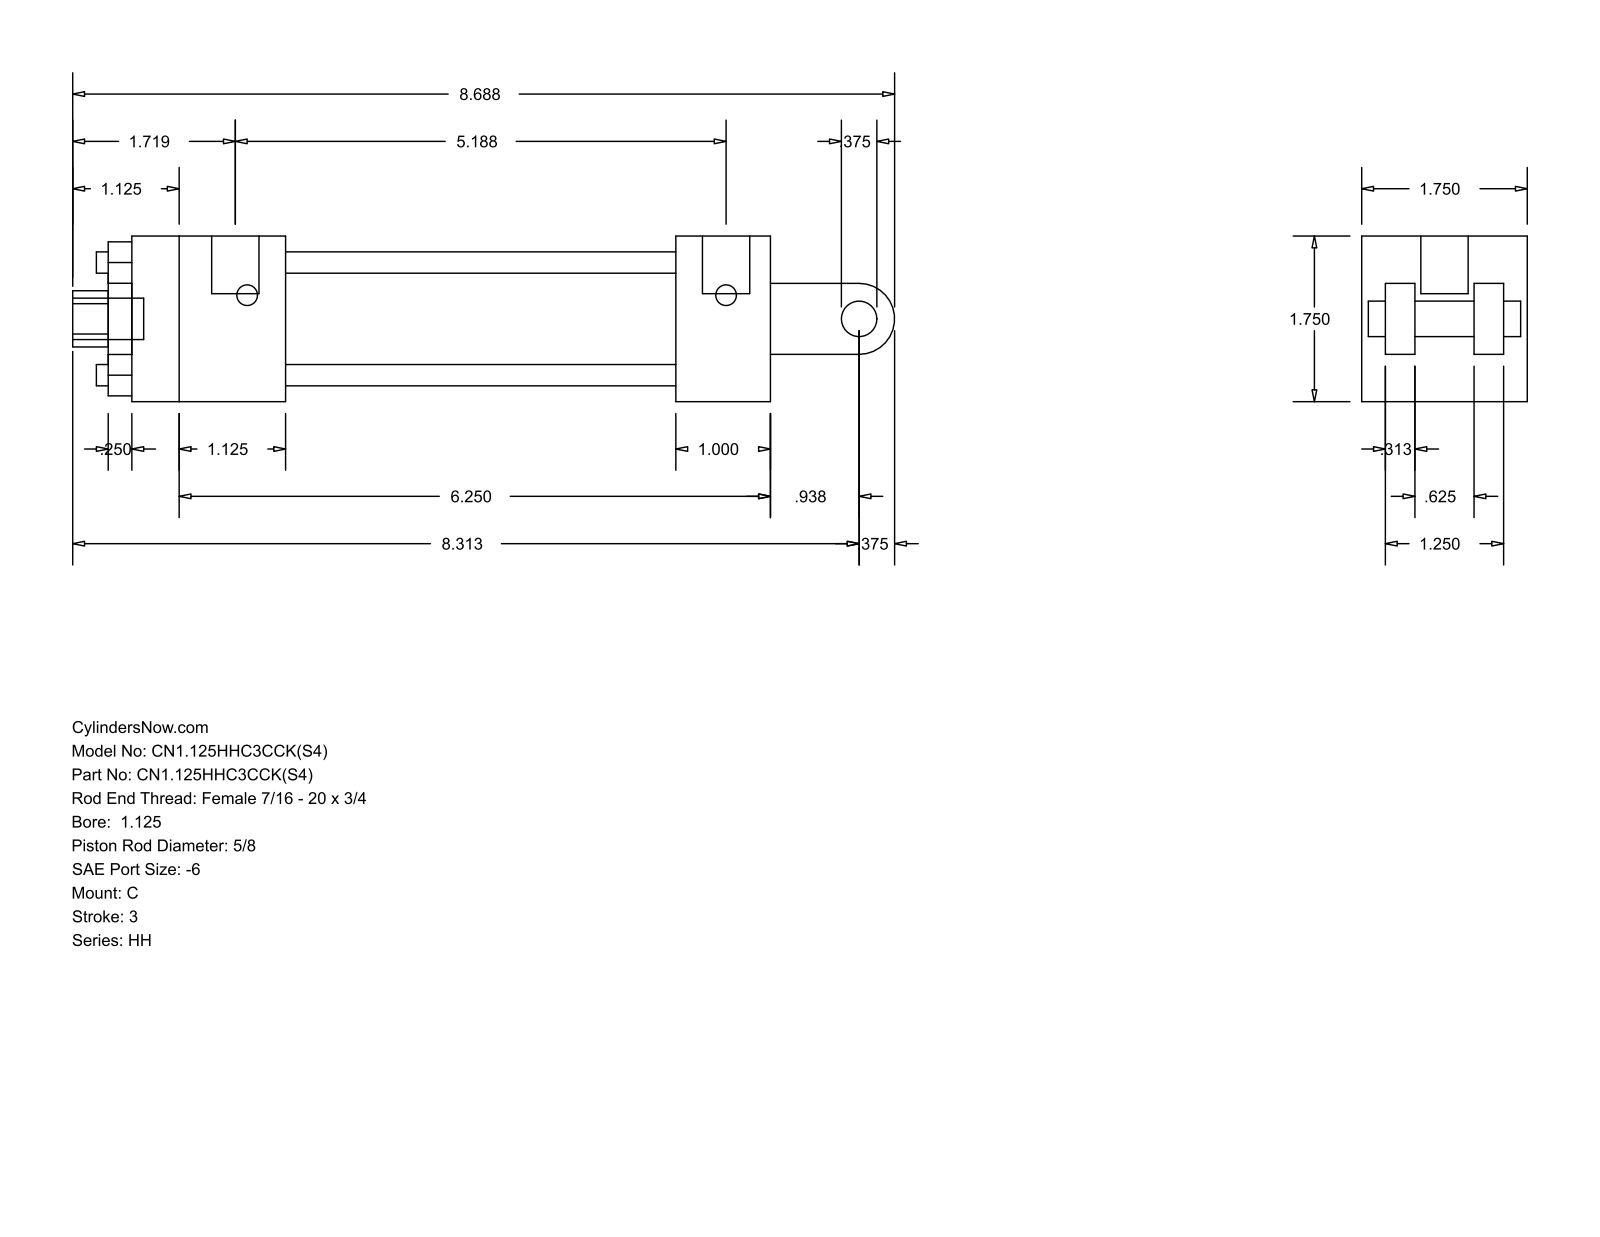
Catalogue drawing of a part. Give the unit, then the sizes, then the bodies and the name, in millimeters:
Units: millimetres
Overall size (bounding box): 220.66 × 44.45 × 44.45
Round holes (diameter × count): ⌀5.71 ×4, ⌀5.56 ×2, ⌀12.7 ×1, ⌀15.88 ×1, ⌀28.57 ×1, ⌀34.92 ×1
Round bosses / shafts (diameter × count): ⌀5.56 ×2, ⌀12.7 ×1, ⌀11.11 ×1, ⌀9.53 ×1
Partial cylindrical surfaces — rounded edges, fillets, slot ends (radius × count): R7.54 ×1, R9.53 ×1
Main face-to-face distances: 44.46, 6.35, 31.76, 14.29, 12.7, 30.17, 38.11, 7.94, 23.82, 41.27
Hole centre spacings: 21.37, 30.22, 42.74
Bodies: 0 solids, 99 faces (70 planar, 29 cylindrical, 0 other)
Part name (STEP PRODUCT): HH_C__0112_0.625
STEP written by: GSSL Pune (CONFIG_CONTROL_DESIGN)
